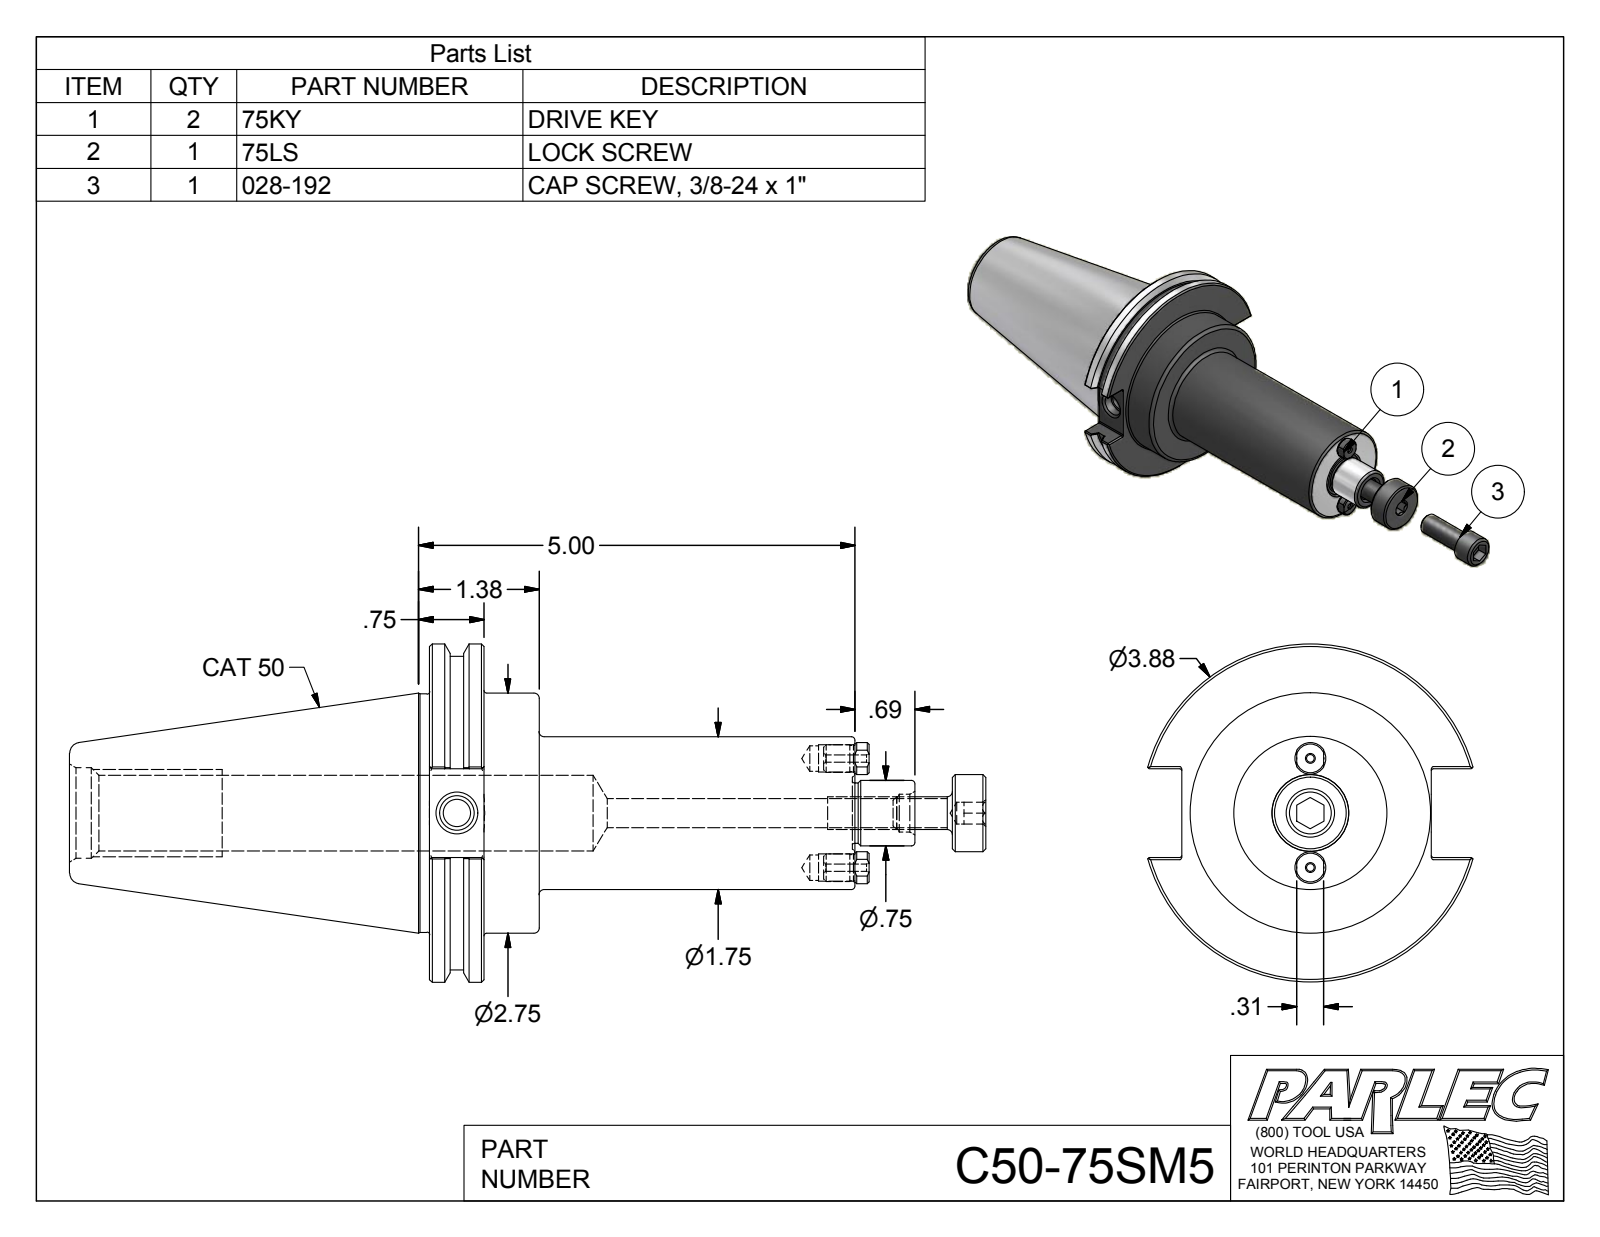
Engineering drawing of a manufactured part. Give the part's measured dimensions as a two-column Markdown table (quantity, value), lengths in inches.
| quantity | value |
| --- | --- |
| part name | C50-75SM5; C50-75SM5-1; 75KY; 75LS (+1 more) |
| STEP written by | Autodesk Inventor 2018 (AUTOMOTIVE_DESIGN) |
| units | inches |
| bodies | 5 solids, 177 faces (68 planar, 48 cylindrical, 61 other) |
| overall size | 13.019 × 3.875 × 3.729 |
| volume | 32.64 in³ |
| surface area | 114.3 in² |
| round holes (diameter × count) | 0.084 × 2, 0.292 × 2, 0.312 × 2, 0.25 × 1, 0.315 × 1, 0.33 × 1, 0.399 × 1, 0.43 × 1, 0.865 × 1, 1.038 × 1 |
| round bosses / shafts (diameter × count) | 0.318 × 2, 0.3 × 2, 3.875 × 1, 3.594 × 1, 2.75 × 1, 2.73 × 1, 1.75 × 1, 0.88 × 1 |
| partial cylindrical surfaces (radius × count) | 0.02 × 12, 0.182 × 2 |
| main face-to-face distances | 0.625, 1.255, 0.63, 4.75, 5.375, 4.12, 4.125, 5.38, 9.5, 10.997 |
| hole center spacings | 0.625, 0.625, 1.25 |
